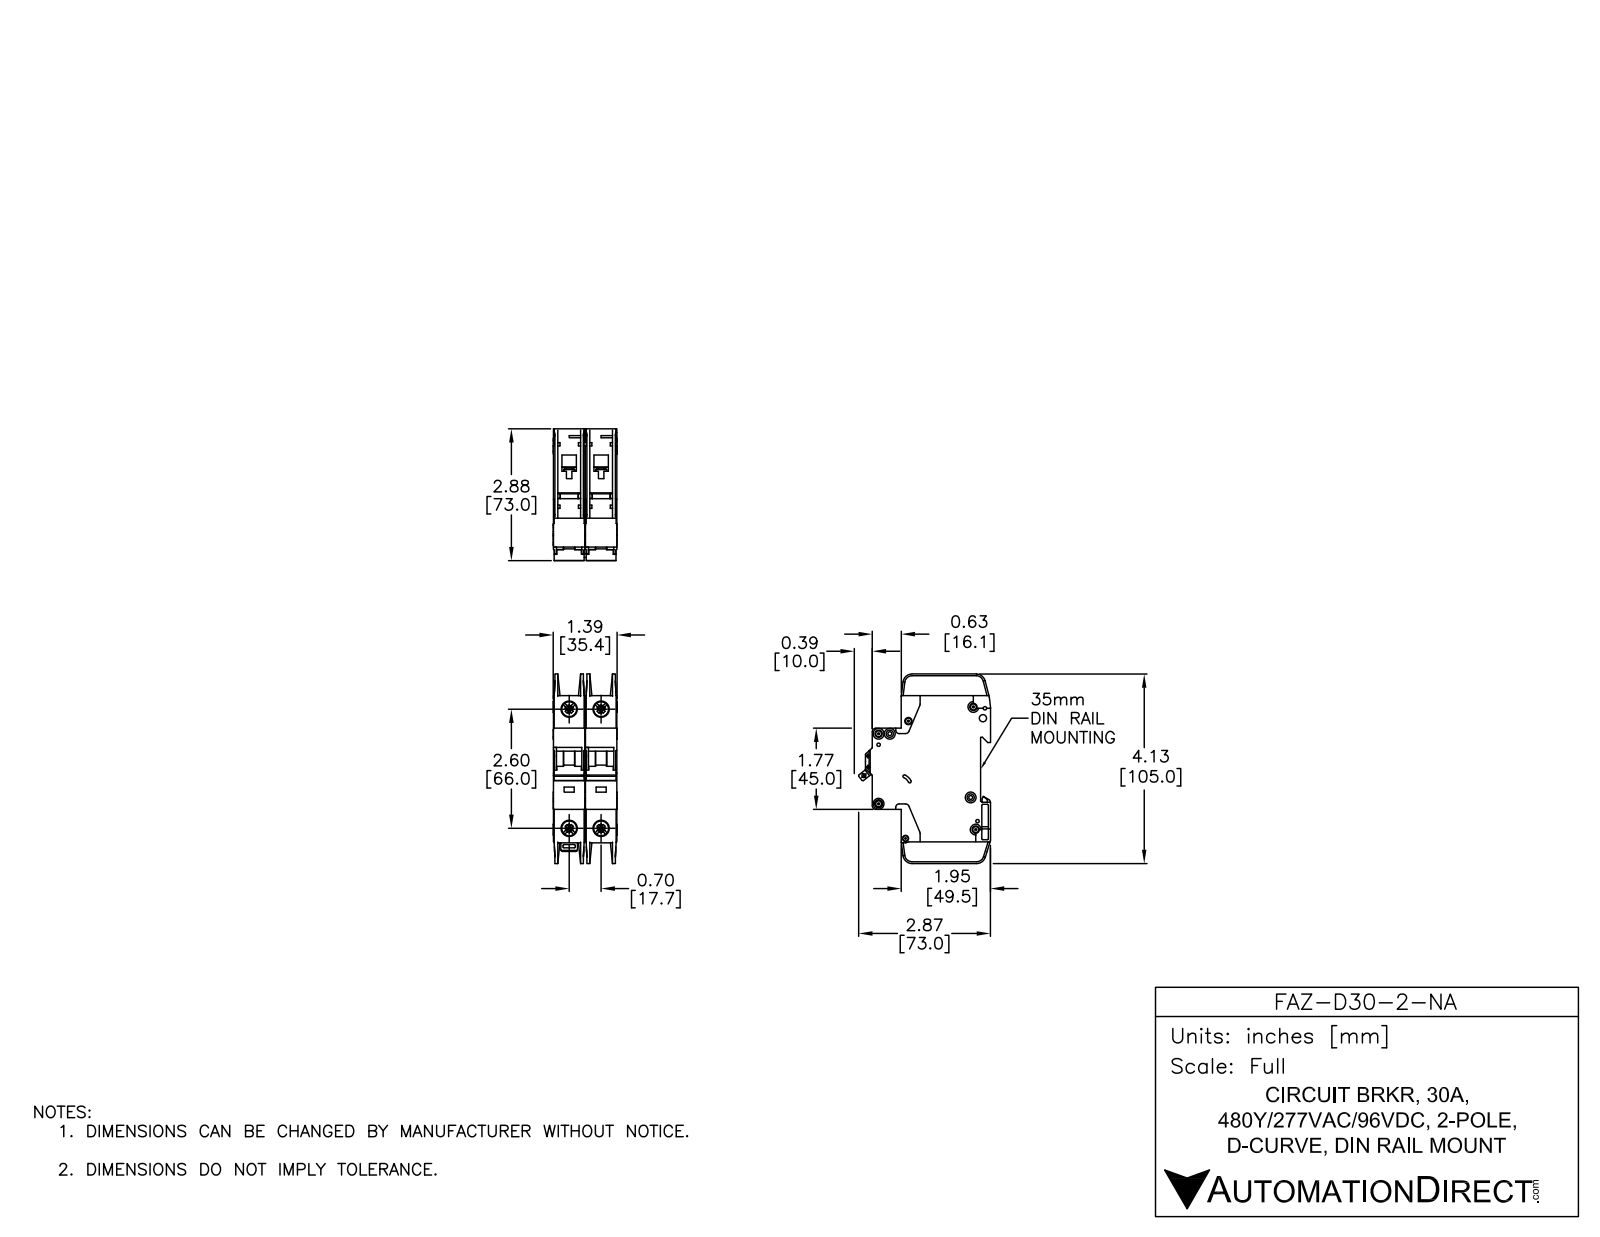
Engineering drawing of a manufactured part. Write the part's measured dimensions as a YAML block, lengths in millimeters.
part_name: "FAZ-D30-2-NA"
step_written_by: "SolidWorks 2014 (AUTOMOTIVE_DESIGN)"
units: millimeters
bodies: {solids: 6, faces: 1568, planar: 818, cylindrical: 526, other: 224}
overall_size: [105, 73.04, 35.4]
volume: 155390
surface_area: 49479
round_holes:
  - {diameter: 3.6, count: 7}
  - {diameter: 7.15, count: 4}
  - {diameter: 8.2, count: 4}
  - {diameter: 1.09, count: 2}
  - {diameter: 1.5, count: 2}
  - {diameter: 4, count: 2}
  - {diameter: 1.9, count: 1}
  - {diameter: 2.15, count: 1}
  - {diameter: 2.2, count: 1}
  - {diameter: 2.55, count: 1}
  - {diameter: 3.3, count: 1}
  - {diameter: 3.4, count: 1}
round_bosses_or_shafts:
  - {diameter: 6, count: 7}
  - {diameter: 2.5, count: 2}
partial_cylinders:
  - {radius: 0.25, count: 47}
  - {radius: 0.5, count: 24}
  - {radius: 1, count: 18}
  - {radius: 2, count: 12}
  - {radius: 5, count: 5}
  - {radius: 1.8, count: 4}
  - {radius: 4, count: 4}
  - {radius: 0.2, count: 2}
face_to_face_distances: [17.7, 17.5, 0.7, 15.05, 2.45, 1.75, 15.75, 13.3, 35.2, 17]
hole_center_spacings: [6.2, 17.7, 66, 68.33, 5.19, 6.1, 8.19, 8.56]
